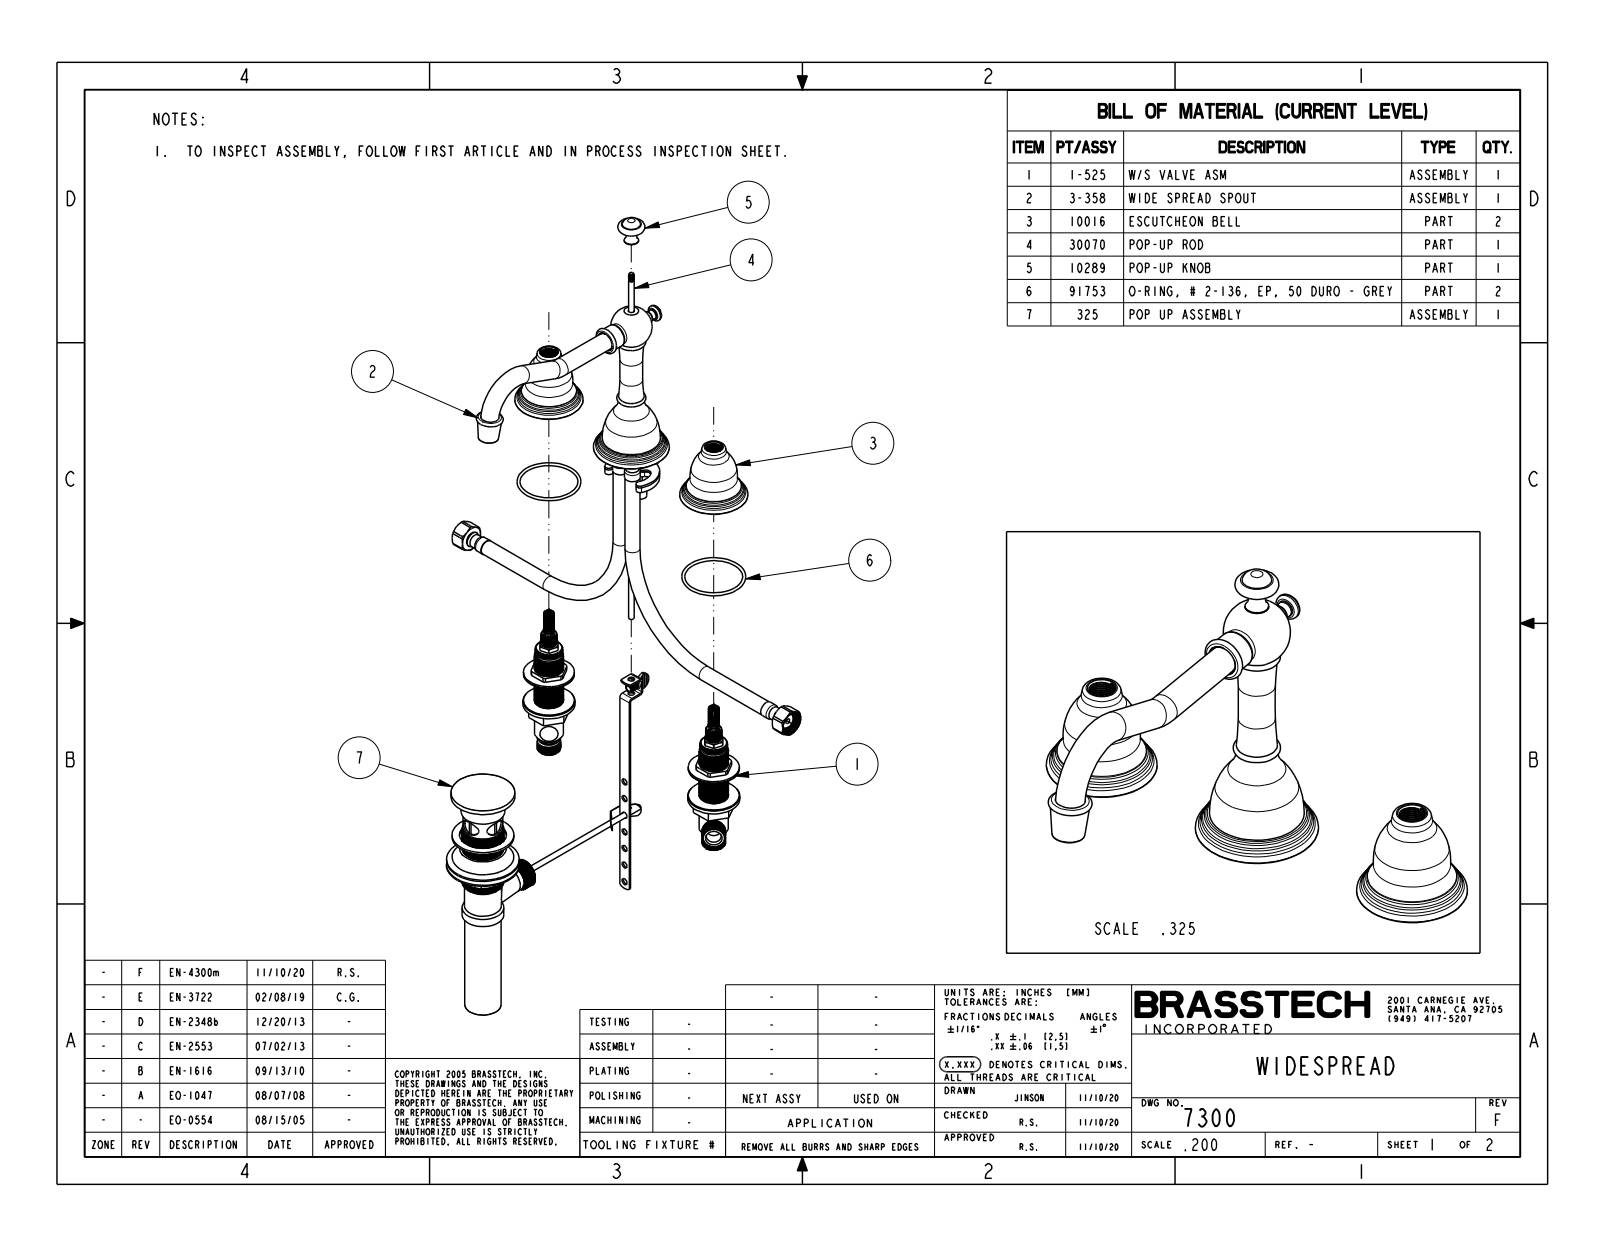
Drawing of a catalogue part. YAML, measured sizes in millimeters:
part_name: "7300"
step_written_by: "CREO PARAMETRIC BY PTC INC, 2018400 (CONFIG_CONTROL_DESIGN)"
units: millimeters
bodies: {solids: 3, faces: 156, planar: 16, cylindrical: 22, other: 118}
overall_size: [262.6, 219.6, 167.1]
volume: 303500
surface_area: 52230
round_bosses_or_shafts:
  - {diameter: 59.4, count: 2}
  - {diameter: 15.9, count: 2}
  - {diameter: 66, count: 1}
  - {diameter: 20.7, count: 1}
  - {diameter: 14.3, count: 1}
  - {diameter: 12.7, count: 1}
  - {diameter: 10.3, count: 1}
  - {diameter: 9.1, count: 1}
face_to_face_distances: [51, 9.9, 41.1, 21.6, 157.3, 147.3, 106.2, 163.2, 153.3, 112.2]
